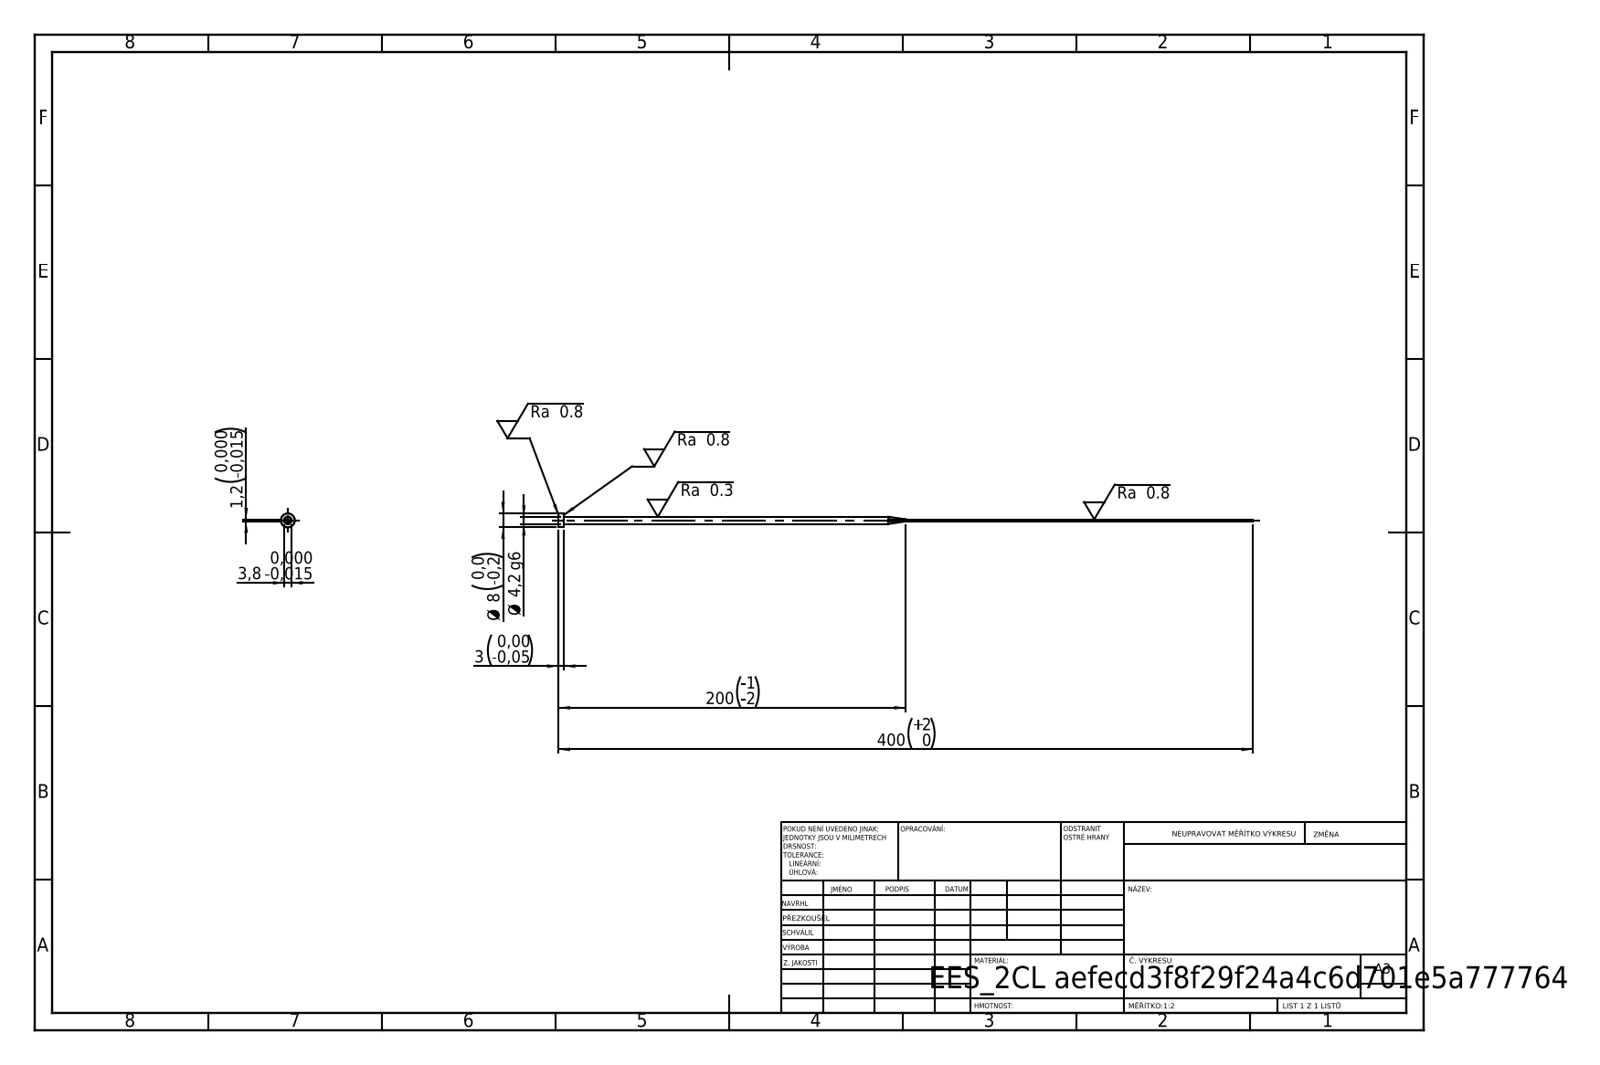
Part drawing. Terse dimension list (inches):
written by: SolidWorks 2019 (CONFIG_CONTROL_DESIGN)
unit: in
bodies: 1 solid, 15 faces (7 planar, 4 cylindrical, 4 other)
size: 15.748 × 0.315 × 0.315
volume: 0.228 in³; area: 7.356 in²
bosses: 1× ⌀0.315, 1× ⌀0.165
face distances: 0.047, 0.15, 0.118, 15.748, 15.63
